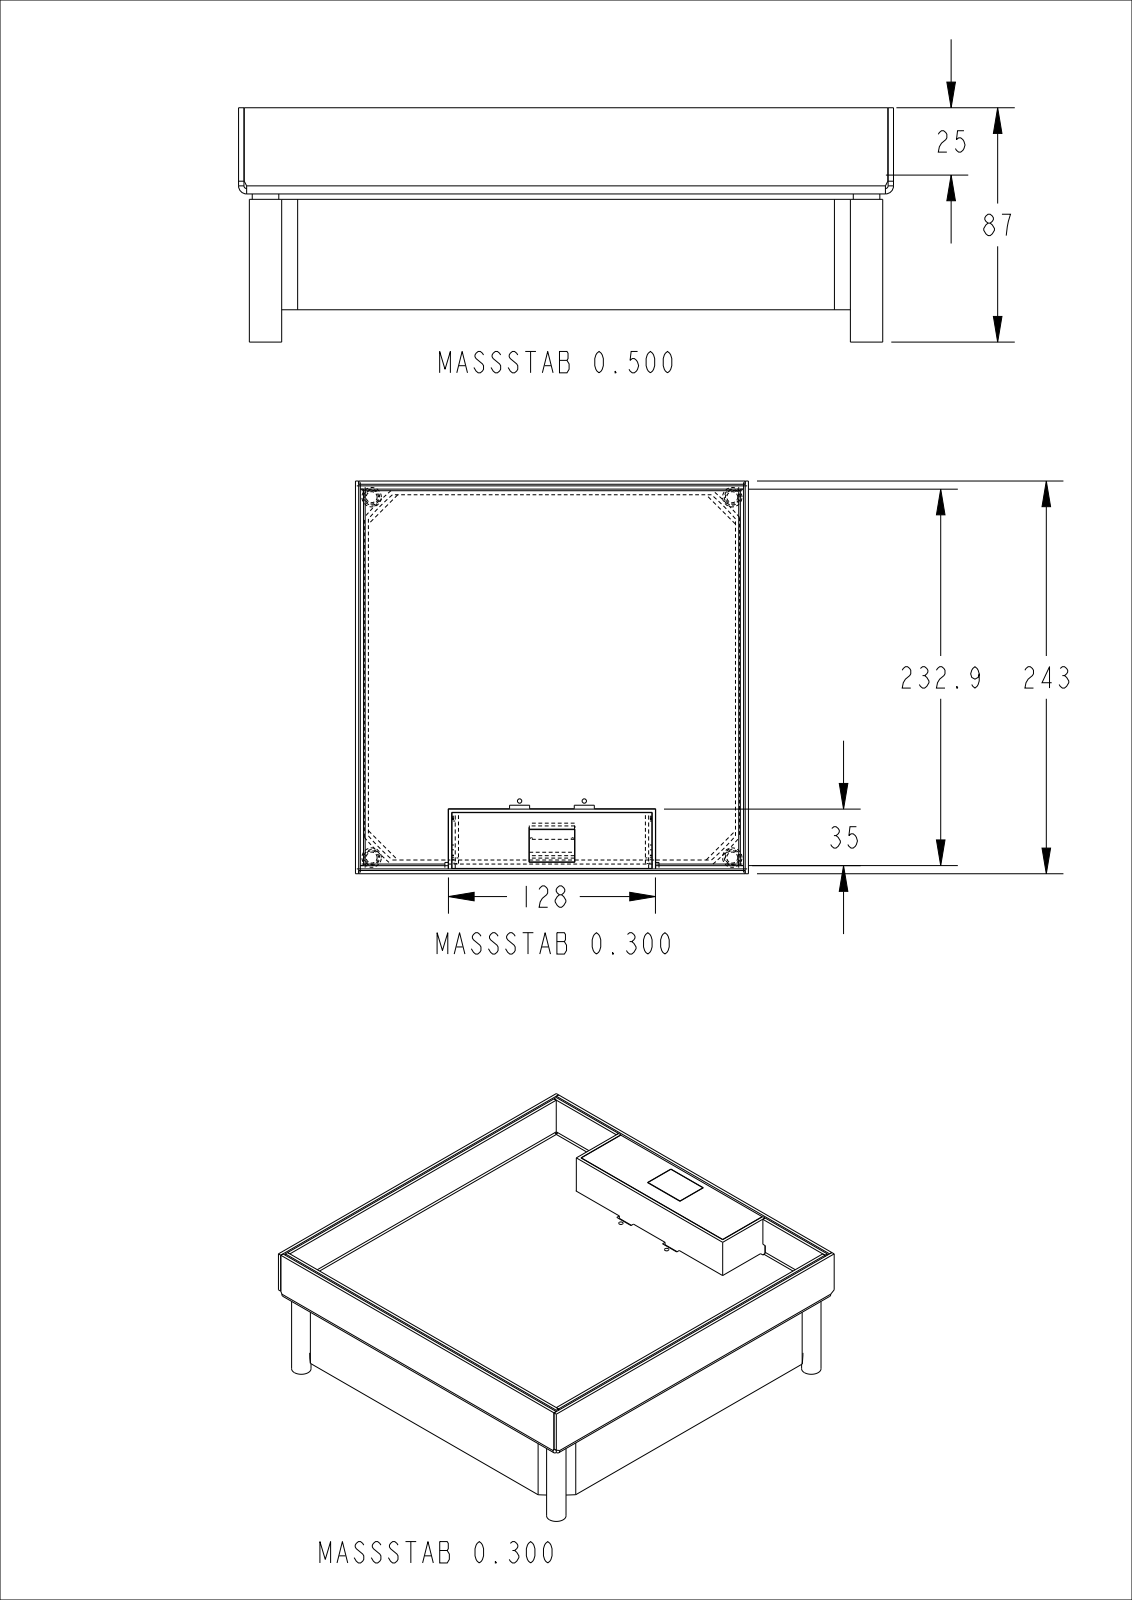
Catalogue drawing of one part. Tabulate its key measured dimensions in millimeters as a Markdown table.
| quantity | value |
| --- | --- |
| part name | T-00627_1; T-00632_1_1; T-00625_1_1; T-00824_ASM_1_ASM (+8 more) |
| STEP written by | CREO PARAMETRIC BY PTC INC, 2022281 (AUTOMOTIVE_DESIGN) |
| units | millimeters |
| bodies | 10 solids, 287 faces (216 planar, 63 cylindrical, 8 other) |
| overall size | 243 × 243 × 87 |
| volume | 343 872 mm³ |
| surface area | 337 570 mm² |
| round holes (diameter × count) | 6.8 × 4, 8.5 × 4, 2.7 × 2 |
| round bosses / shafts (diameter × count) | 12 × 4, 9.85 × 4 |
| partial cylindrical surfaces (radius × count) | 1 × 8, 3 × 8, 6.6 × 1, 150 × 1, 152.5 × 1 |
| main face-to-face distances | 2, 3, 2.5, 235, 5, 238, 6, 1, 241, 232 |
| hole center spacings | 223, 97.97, 136.08, 209.08, 229.43, 315.37, 40 |
